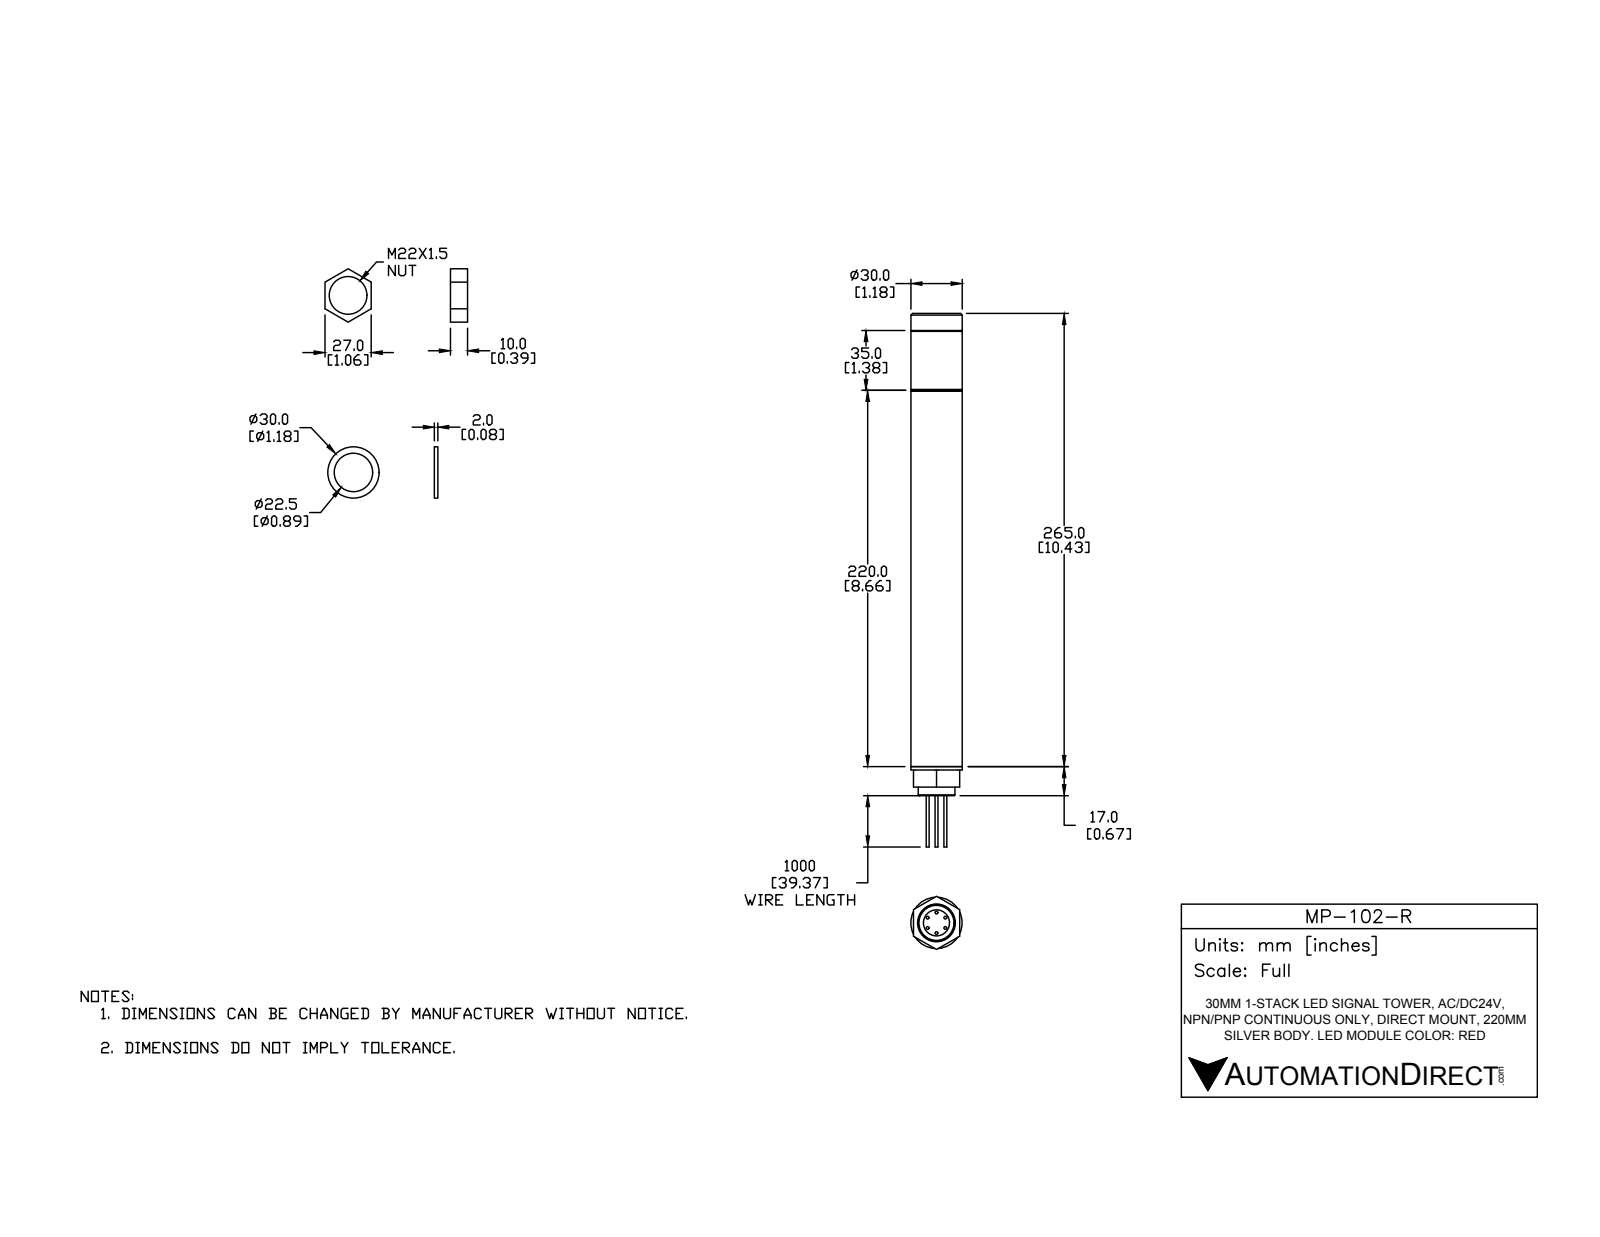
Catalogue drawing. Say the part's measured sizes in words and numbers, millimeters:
The part is named "MP-102-R". Its 3-D file was written by "SolidWorks 2016 (AUTOMOTIVE_DESIGN)". It is 12 solids with 95 faces: 47 planar, 36 cylindrical and 12 other. Overall it measures 312 by 31.18 by 30 millimeters. Its volume is 183 274 cubic millimeters and its surface area 39 388 square millimeters. Round holes: 1 of diameter 3.2, 1 of diameter 7.7, 1 of diameter 15.3, 1 of diameter 20.7, 1 of diameter 22. Round bosses or shafts: 6 of diameter 1.7, 1 of diameter 30, 1 of diameter 21.5, 1 of diameter 5. The main face-to-face distances are 35, 222, 45, 267, 220, 255, 10, 232, 2, 257.
